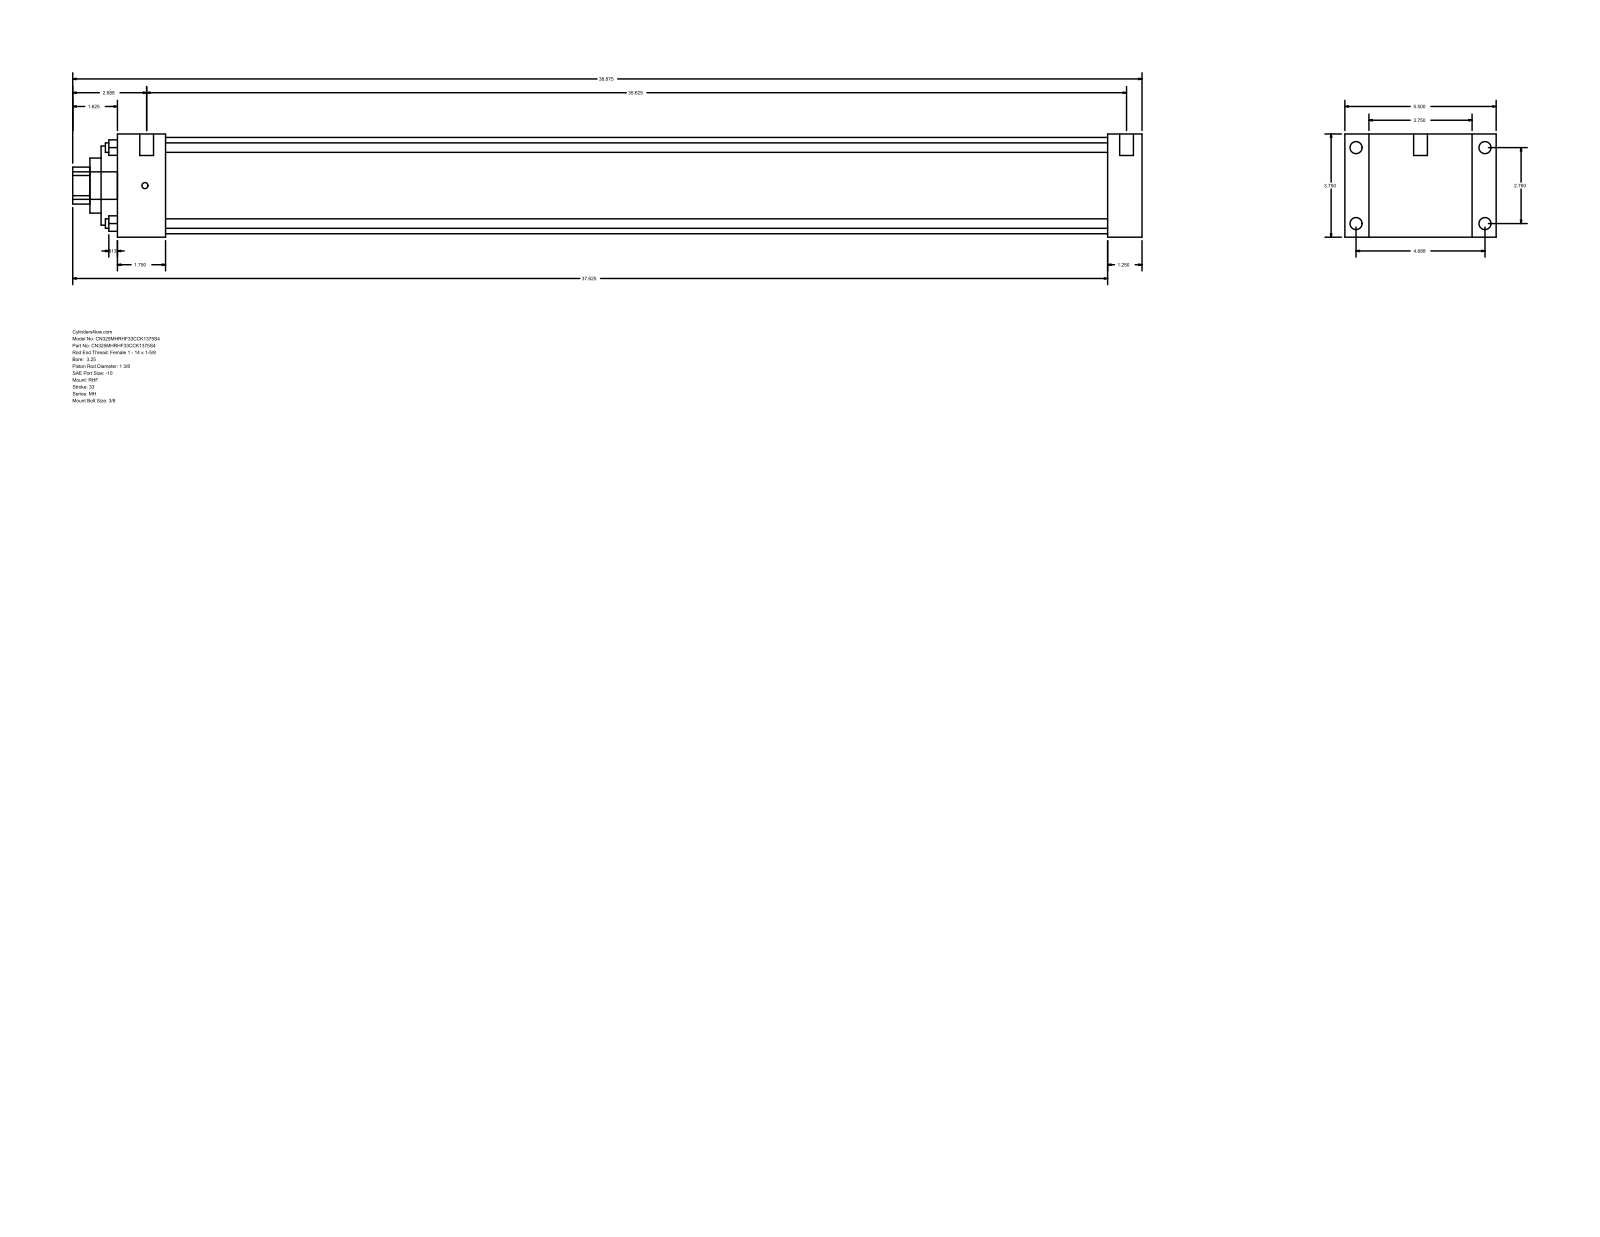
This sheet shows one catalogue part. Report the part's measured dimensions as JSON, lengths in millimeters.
{"part_name": "MH_RHF__0325_1.375", "step_written_by": "GSSL Pune (CONFIG_CONTROL_DESIGN)", "units": "millimeters", "bodies": {"solids": 0, "faces": 90, "planar": 61, "cylindrical": 29, "other": 0}, "overall_size": [987.42, 139.7, 95.25], "round_holes": [[8.76, 4], [34.92, 1], [50.8, 1], [73.03, 1], [88.9, 1]], "round_bosses_or_shafts": [[11.13, 4], [5.56, 4], [12.7, 2], [25.4, 1]], "partial_cylinders_radius": [[17.06, 1]], "face_to_face_distances": [95.24, 31.75, 22.23, 117.47, 914.4, 946.15, 139.7, 44.45, 869.95, 901.7], "hole_center_spacings": [49.57, 70.1, 99.14]}
